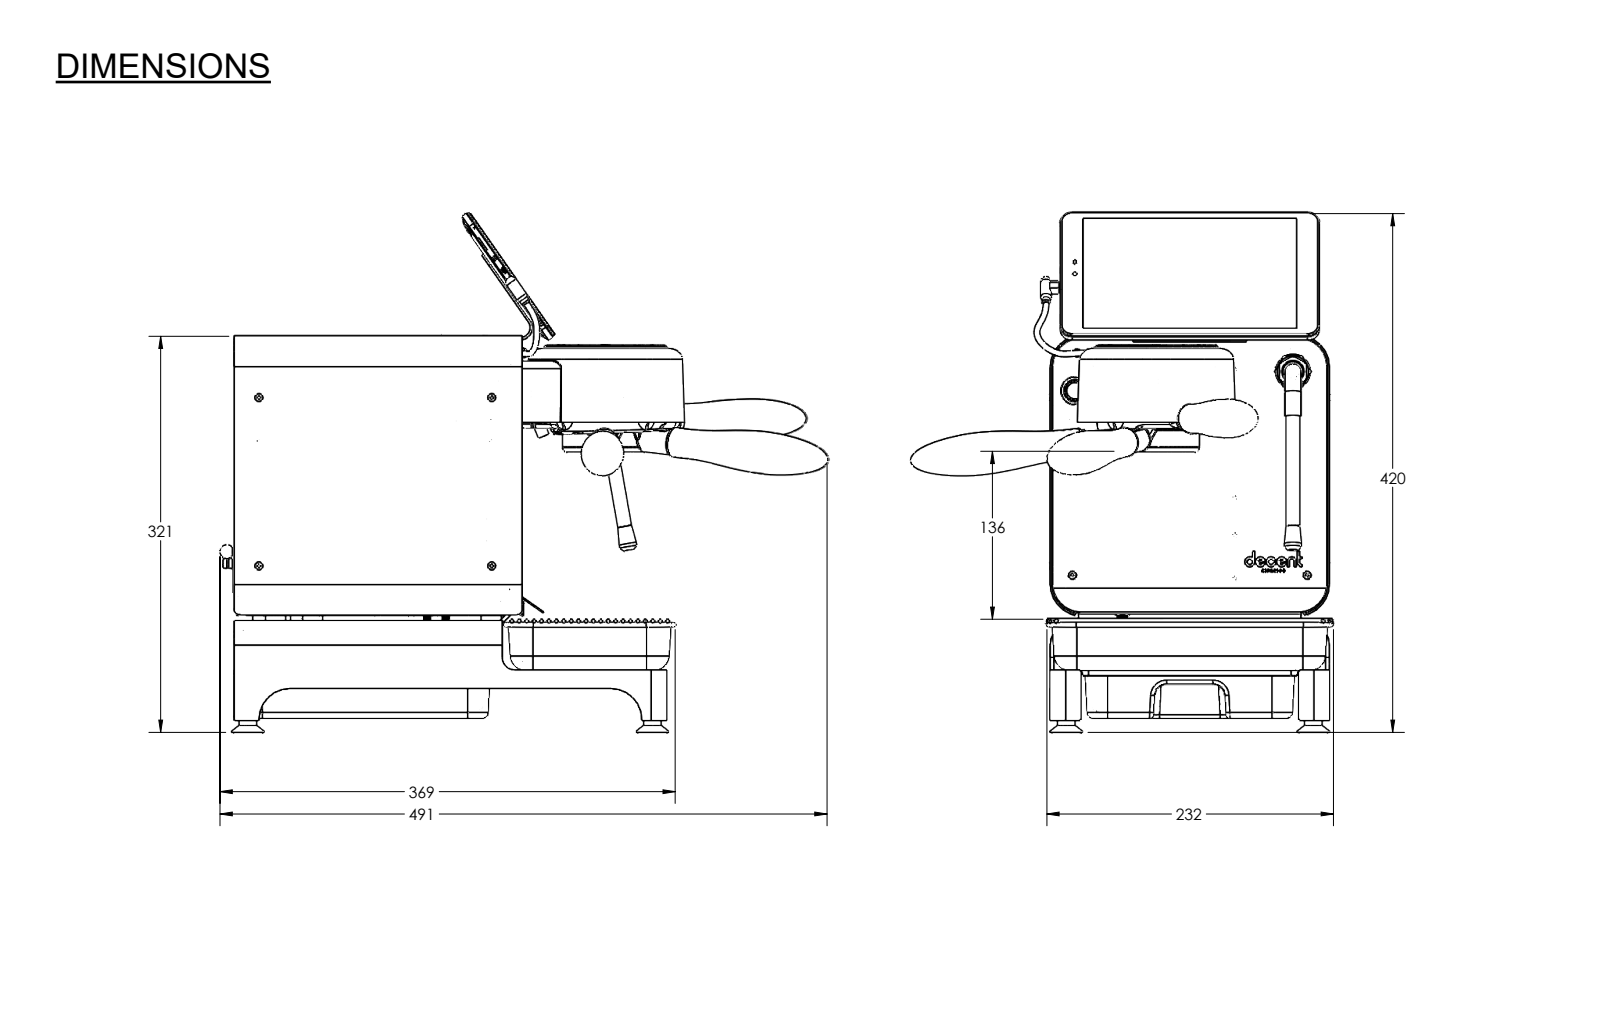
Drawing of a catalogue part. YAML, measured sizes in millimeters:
part_name: "73529 DE1 Drip Tray Cover; 73526 DE1 Leg Base; 73522 DE1 PCB Partition Plate; 73556 DE1 Group Head External Cover_-001 (+8 more)"
step_written_by: "SolidWorks 2017 (AUTOMOTIVE_DESIGN)"
units: millimeters
bodies: {solids: 234, faces: 9295, planar: 3911, cylindrical: 3089, other: 2295}
overall_size: [491.85, 419.76, 241.54]
volume: 2794000
surface_area: 2136000
round_holes:
  - {diameter: 2, count: 122}
  - {diameter: 4.22, count: 35}
  - {diameter: 3.4, count: 31}
  - {diameter: 2.46, count: 27}
  - {diameter: 1.2, count: 21}
  - {diameter: 3.2, count: 19}
  - {diameter: 3.3, count: 16}
  - {diameter: 4, count: 16}
  - {diameter: 2.46, count: 11}
  - {diameter: 3.5, count: 9}
  - {diameter: 3.6, count: 9}
  - {diameter: 5, count: 9}
round_bosses_or_shafts:
  - {diameter: 3, count: 58}
  - {diameter: 4.2, count: 35}
  - {diameter: 6.35, count: 31}
  - {diameter: 0.8, count: 21}
  - {diameter: 5.28, count: 20}
  - {diameter: 3.91, count: 15}
  - {diameter: 5.27, count: 11}
  - {diameter: 6, count: 10}
partial_cylinders:
  - {radius: 2, count: 139}
  - {radius: 0.5, count: 118}
  - {radius: 1, count: 88}
  - {radius: 0.1, count: 75}
  - {radius: 2.5, count: 68}
  - {radius: 0.35, count: 60}
  - {radius: 5, count: 53}
  - {radius: 10, count: 48}
face_to_face_distances: [2, 4, 1.5, 1, 6, 3, 224.5, 5, 218.5, 220.5]
hole_center_spacings: [35, 46, 130, 188.5, 11, 45, 51.25, 54]
